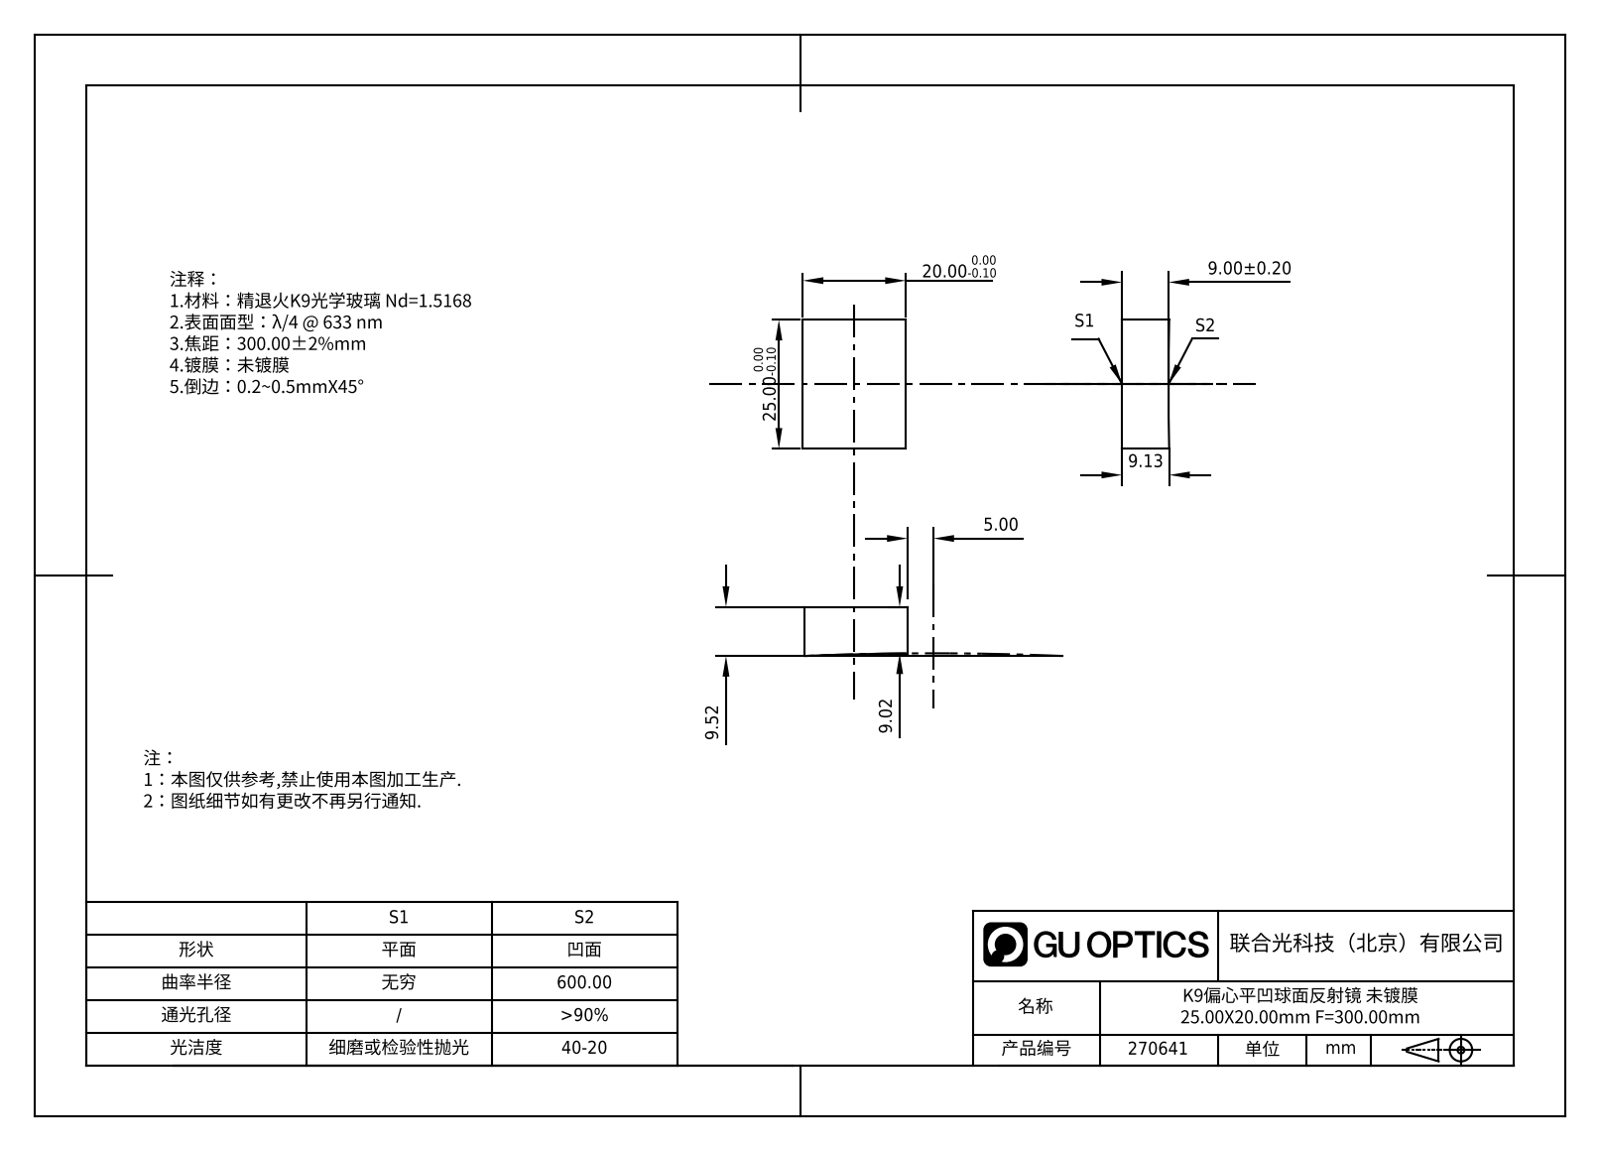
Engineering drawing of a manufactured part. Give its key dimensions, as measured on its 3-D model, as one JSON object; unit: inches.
{"part_name": "270641", "step_written_by": "SolidWorks 2020 (CONFIG_CONTROL_DESIGN)", "units": "inches", "bodies": {"solids": 1, "faces": 7, "planar": 5, "cylindrical": 0, "other": 2}, "overall_size": [0.984, 0.787, 0.38], "volume_in3": 0.282, "surface_area_in2": 2.852, "face_to_face_distances": [0.787, 0.984]}
